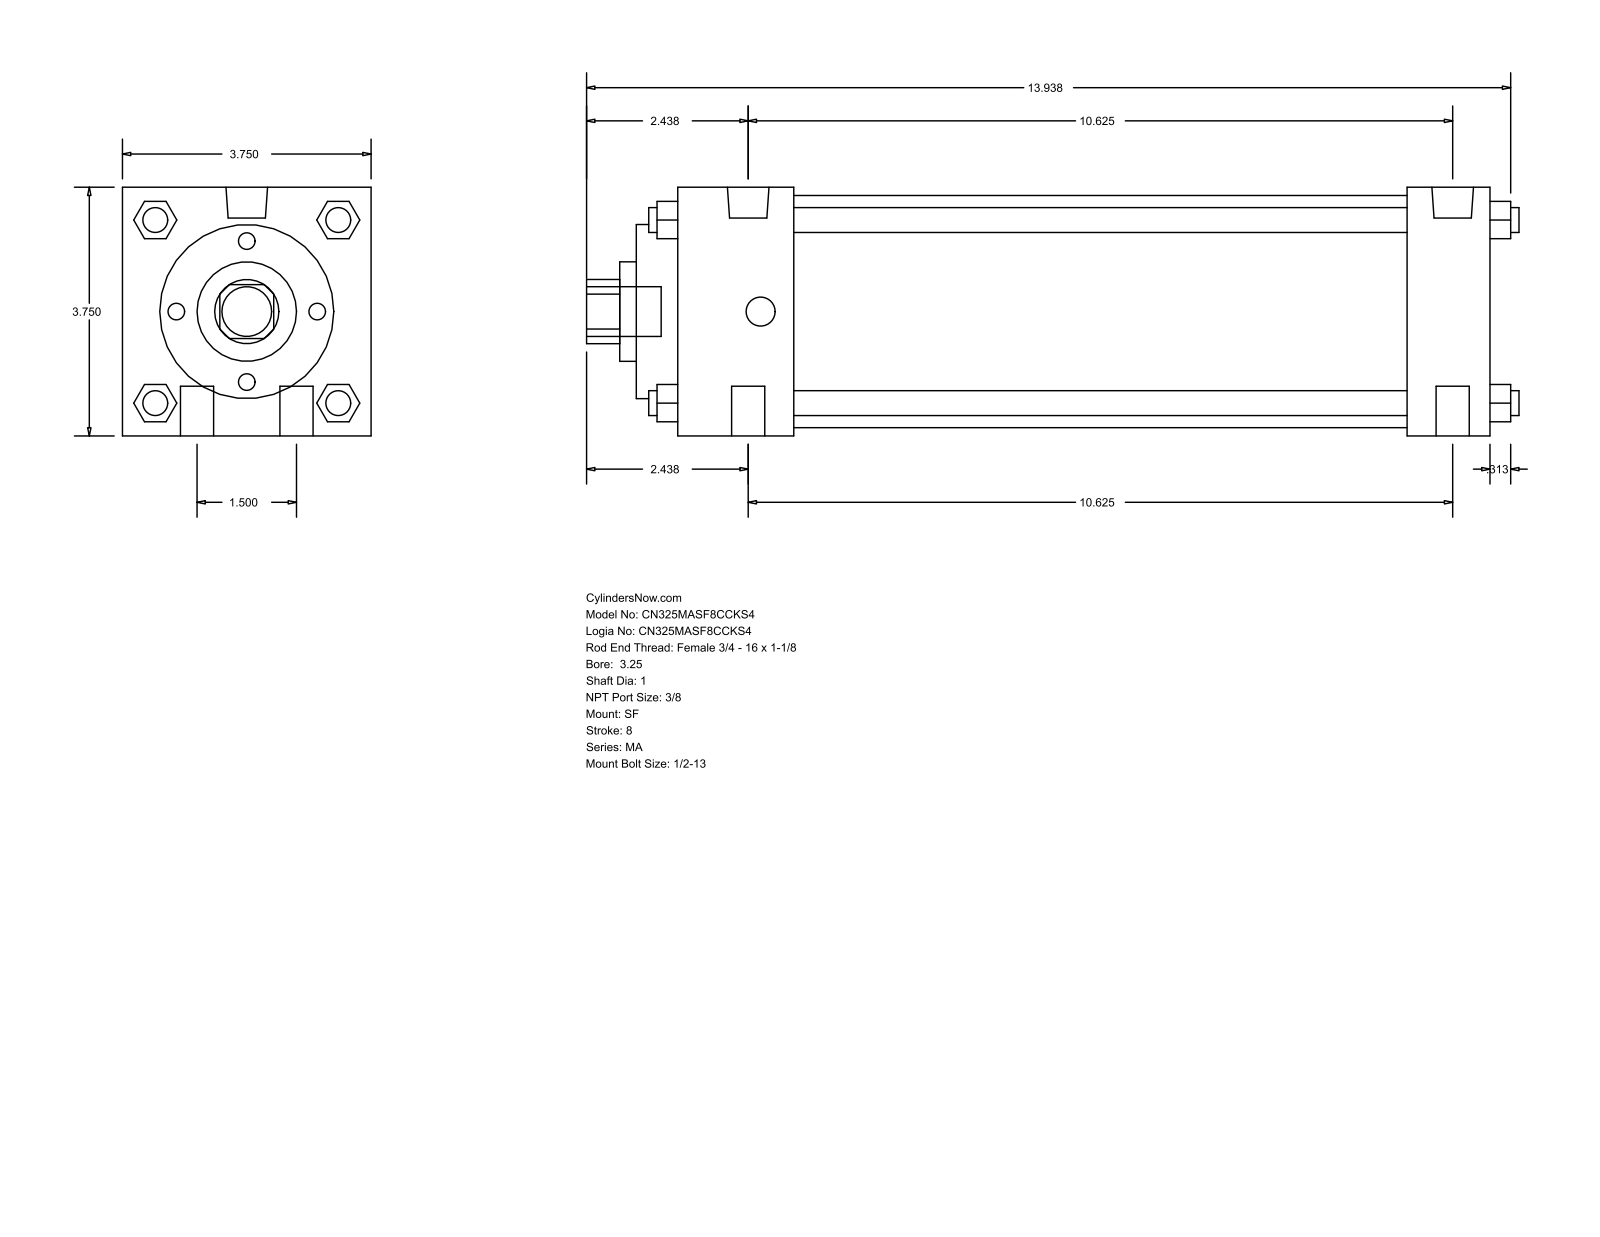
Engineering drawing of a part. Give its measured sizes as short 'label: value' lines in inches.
name: MA_SF__0325_1
written by: GSSL Pune (CONFIG_CONTROL_DESIGN)
unit: in
bodies: 0 solids, 126 faces (95 planar, 31 cylindrical, 0 other)
size: 14.063 × 3.75 × 3.75
holes: 1× ⌀1, 1× ⌀1.5, 1× ⌀2.625, 1× ⌀3.5
bosses: 4× ⌀0.5, 4× ⌀0.375, 2× ⌀0.627, 2× ⌀0.437, 1× ⌀0.75
rounds: 1× R0.484
face distances: 3.75, 12.25, 12.875, 0.625, 11, 1.25, 1.75, 9.25, 10.5, 2.375
